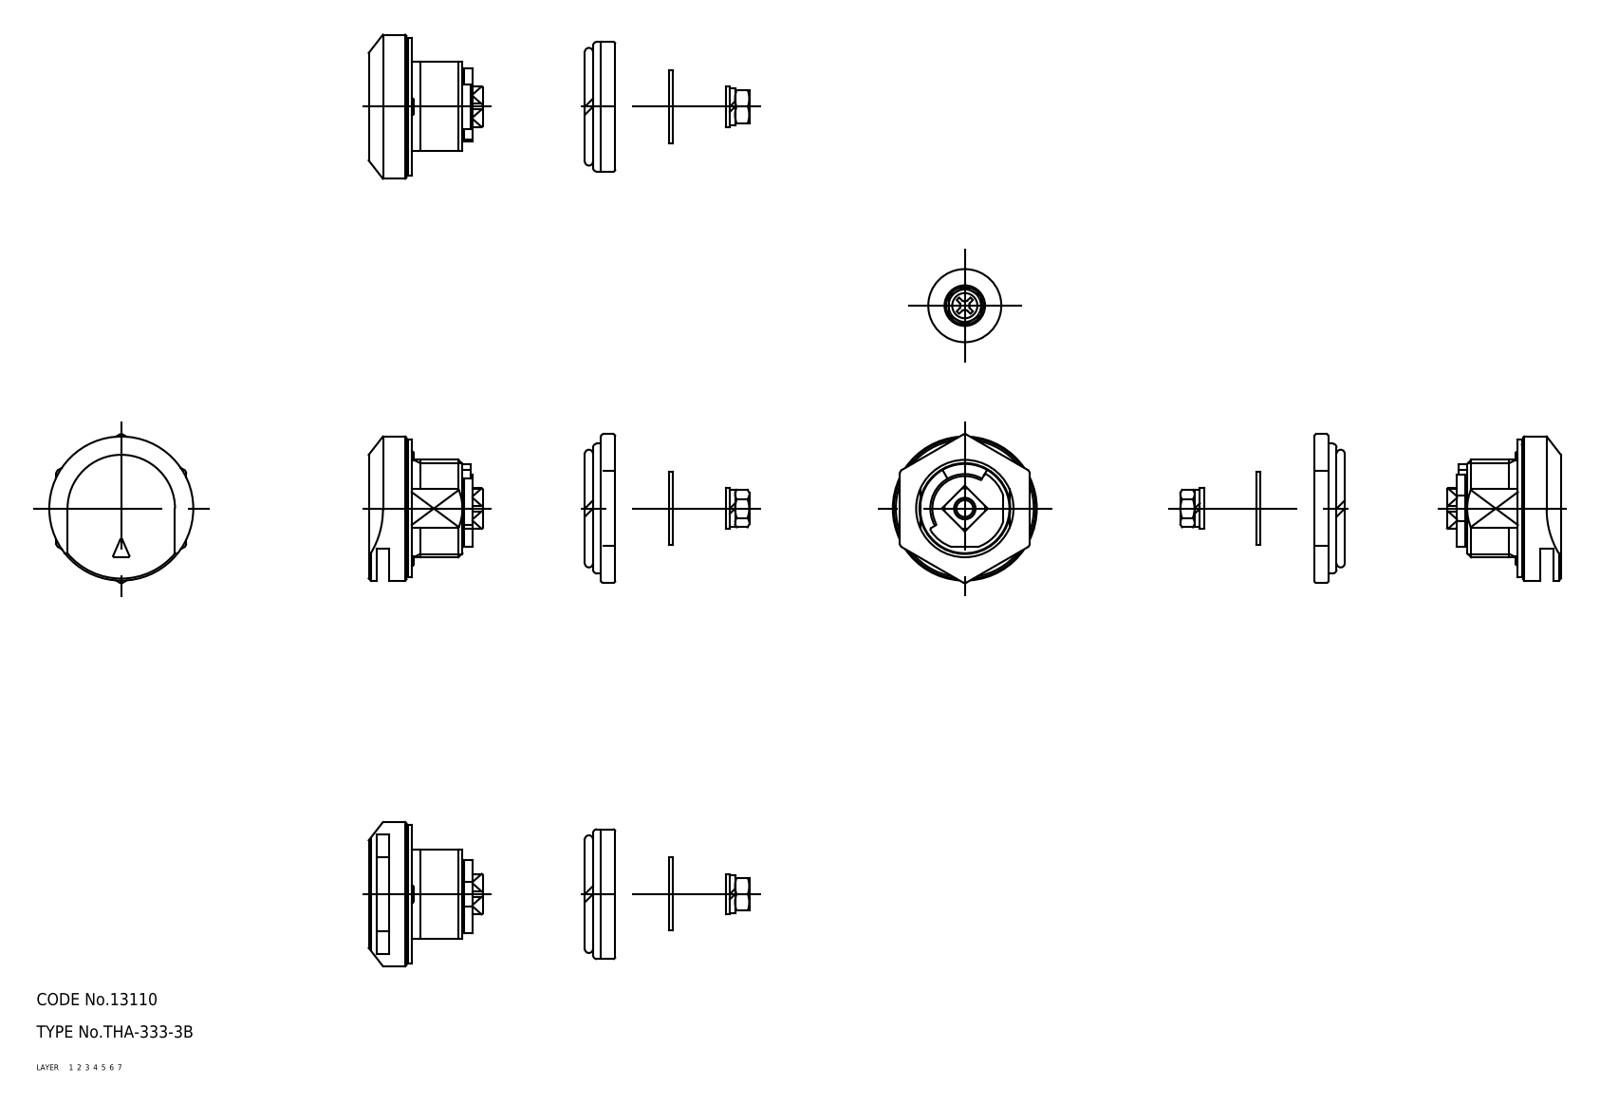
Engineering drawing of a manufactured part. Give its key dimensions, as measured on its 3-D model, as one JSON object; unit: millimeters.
{"part_name": "washer_B; rotor; packing; nut (+3 more)", "step_written_by": "CADfix (AUTOMOTIVE_DESIGN)", "units": "millimeters", "bodies": {"solids": 7, "faces": 258, "planar": 0, "cylindrical": 0, "other": 258}, "overall_size": [36.64, 35.5, 33.9], "volume_mm3": 15486, "surface_area_mm2": 13389}
